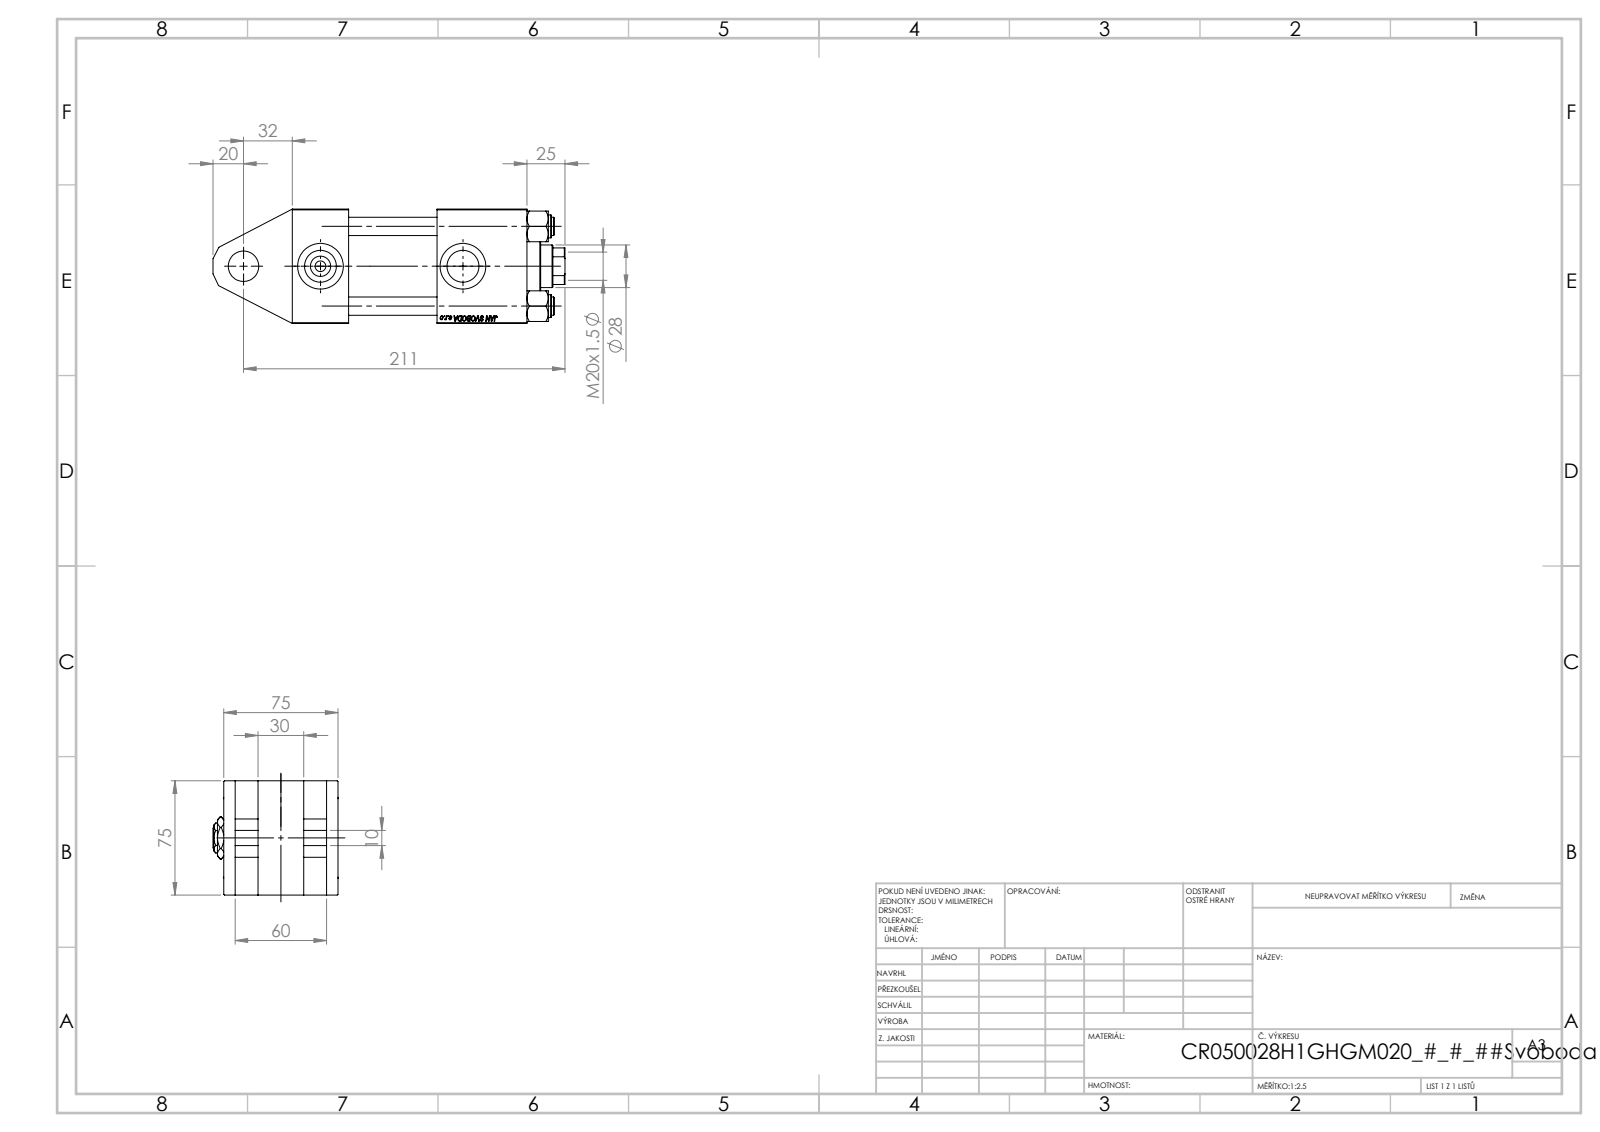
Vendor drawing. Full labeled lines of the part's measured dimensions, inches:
Part name (STEP PRODUCT): V215CR_VCP_H; Zatka_pro_OIL_PORT; V215_VC_A; V215CR_TYCINKA_H (+2 more)
STEP written by: SolidWorks 2019 (CONFIG_CONTROL_DESIGN)
Units: inches
Bodies: 12 solids, 1176 faces (541 planar, 87 cylindrical, 548 other)
Overall size (bounding box): 9.094 × 3.239 × 2.953
Volume: 45.33 in³ · Surface area: 261.2 in²
Round holes (diameter × count): ⌀0.472 ×4, ⌀0.276 ×2, ⌀0.825 ×2, ⌀1.181 ×2, ⌀0.728 ×1, ⌀0.787 ×1, ⌀1.102 ×1, ⌀1.22 ×1, ⌀1.614 ×1, ⌀1.969 ×1, ⌀2.087 ×1
Round bosses / shafts (diameter × count): ⌀0.591 ×4, ⌀2.205 ×1, ⌀1.654 ×1
Partial cylindrical surfaces — rounded edges, fillets, slot ends (radius × count): R0.531 ×1
Main face-to-face distances: 2.953, 2.657, 0.295, 0.886, 2.067, 0.591, 1.772, 4.606, 3.74, 1.457
Hole centre spacings: 1.456, 2.059, 2.912, 1.988, 3.681, 5.669
